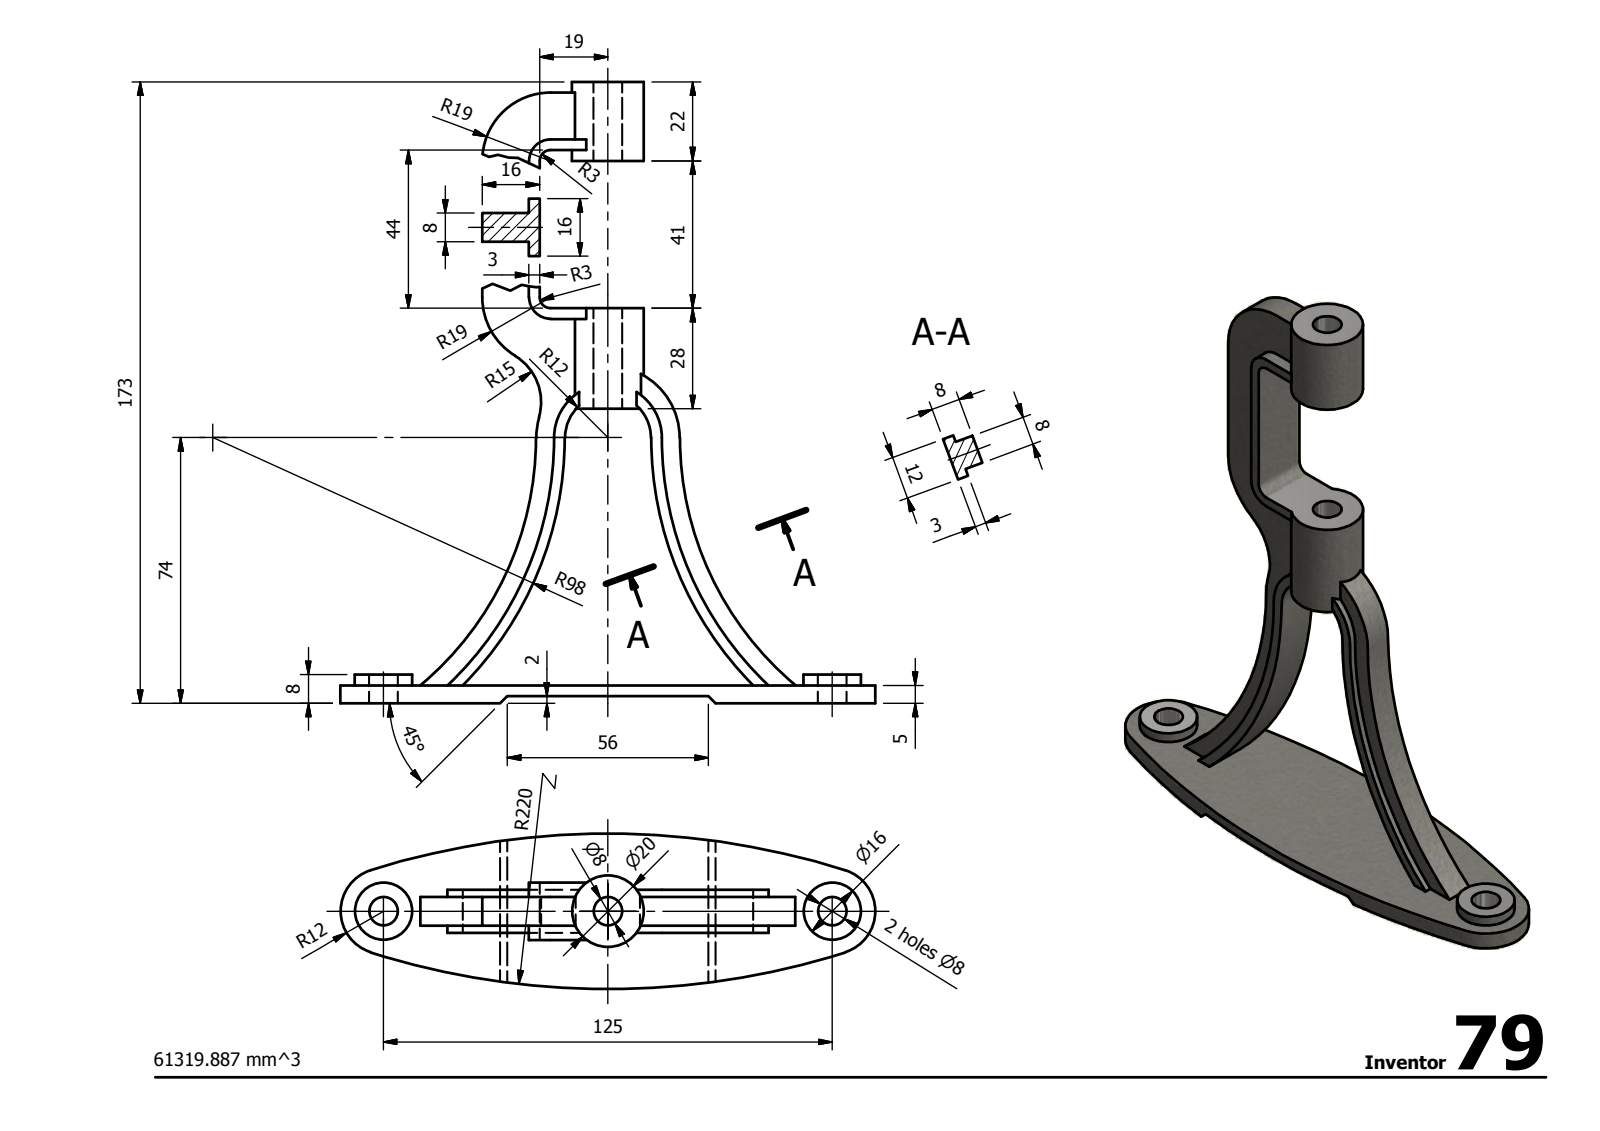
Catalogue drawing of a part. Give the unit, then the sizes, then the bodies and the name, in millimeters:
Units: millimetres
Overall size (bounding box): 173 × 149 × 43.22
Round holes (diameter × count): ⌀8 ×3
Round bosses / shafts (diameter × count): ⌀16 ×2, ⌀20 ×1
Partial cylindrical surfaces — rounded edges, fillets, slot ends (radius × count): R12 ×3, R3 ×2, R6 ×2, R15 ×2, R19 ×2, R90 ×2, R95 ×2, R98 ×2
Main face-to-face distances: 2, 3, 8, 5, 10, 12, 16, 105, 149, 4
Hole centre spacings: 62.5, 125
Volume: 61 319 mm³ · Surface area: 29 553 mm²
Bodies: 1 solid, 69 faces (32 planar, 37 cylindrical, 0 other)
STEP written by: Autodesk Inventor 2014 (AUTOMOTIVE_DESIGN)
